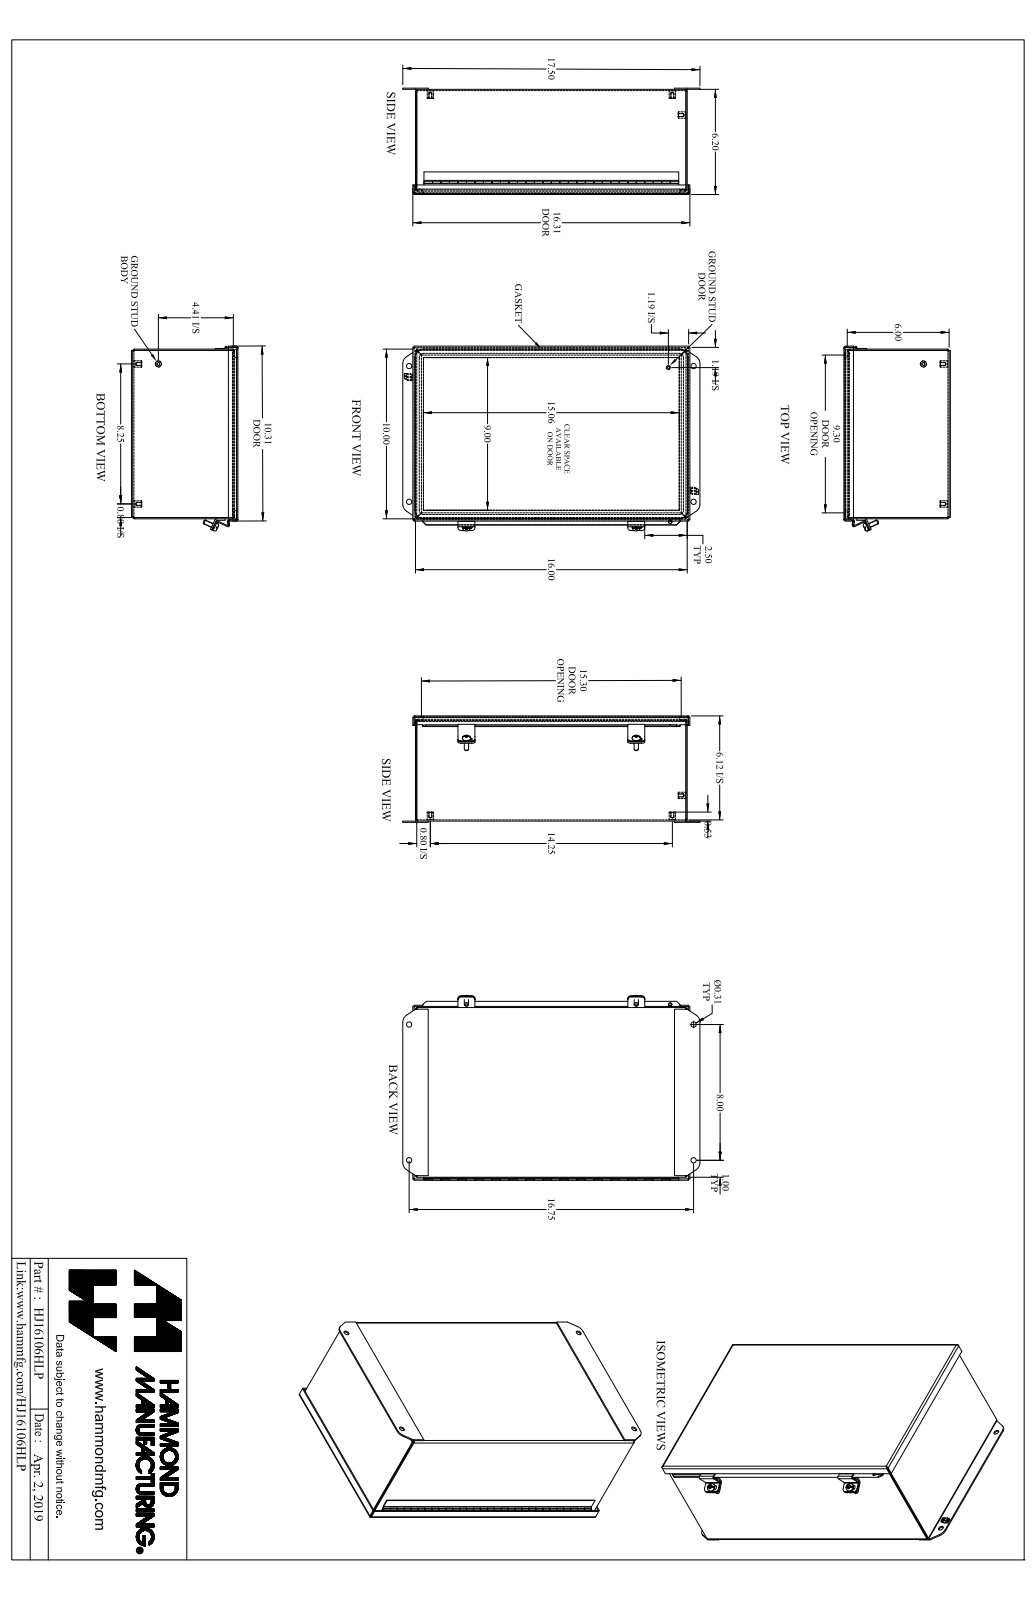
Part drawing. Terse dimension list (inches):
name: HJ16106HLP
written by: SolidWorks 2018 (AUTOMOTIVE_DESIGN)
unit: in
bodies: 20 solids, 837 faces (446 planar, 263 cylindrical, 128 other)
size: 17.5 × 10.896 × 6.269
volume: 56.73 in³; area: 1 595 in²
holes: 5× ⌀0.156, 4× ⌀0.313, 2× ⌀0.213, 1× ⌀0.05
bosses: 5× ⌀0.375, 3× ⌀0.25, 2× ⌀0.48, 1× ⌀0.188, 1× ⌀0.1, 1× ⌀0.045
rounds: 16× R0.25, 13× R0.036, 13× R0.108, 4× R0.01, 4× R0.141, 4× R0.188, 4× R0.499, 4× R0.5
face distances: 0.072, 6.125, 6.197, 9.928, 6.053, 15.928, 10, 9.856, 16, 15.856
hole spacings: 1.257, 8.22, 15.5, 17.5, 8, 8.25, 14.25, 16.465
